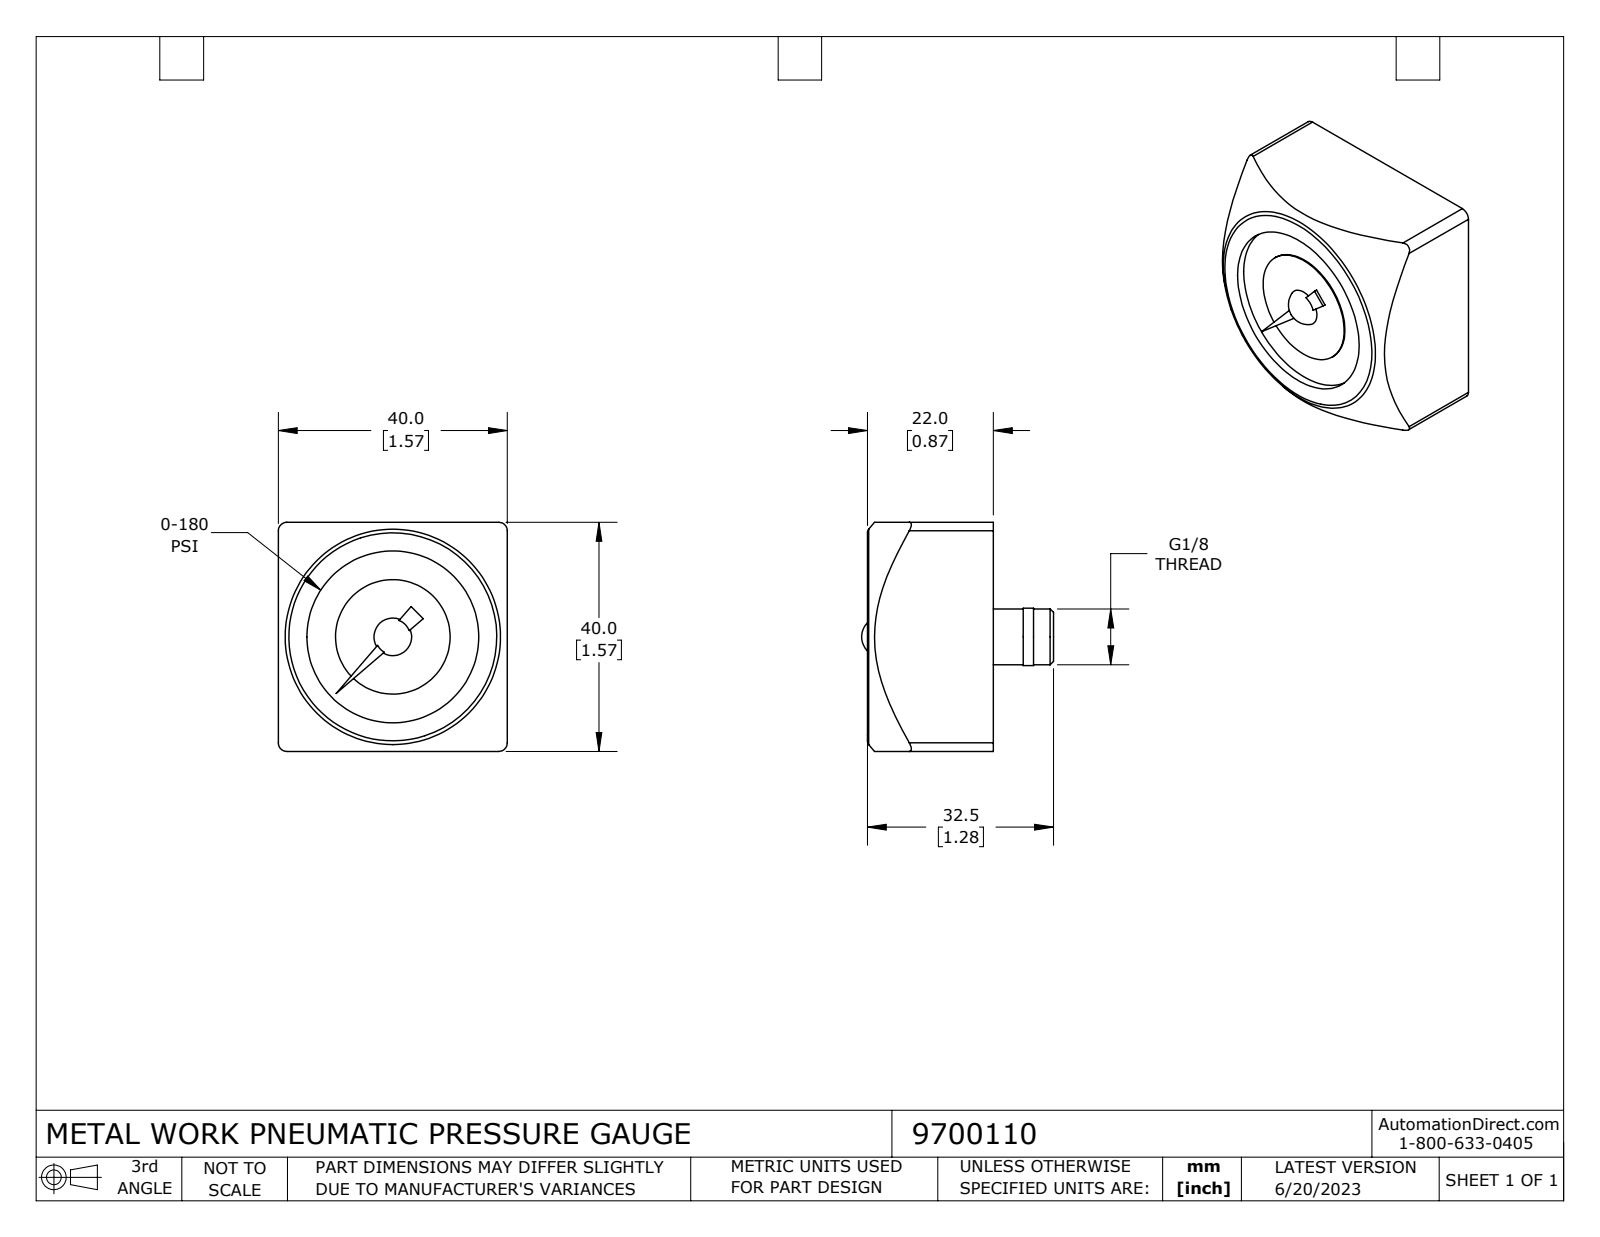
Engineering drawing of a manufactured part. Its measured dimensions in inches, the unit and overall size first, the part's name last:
Units: inches
Overall size (bounding box): 1.575 × 1.575 × 1.319
Round holes (diameter × count): ⌀1.181 ×1
Round bosses / shafts (diameter × count): ⌀0.787 ×1, ⌀0.394 ×1, ⌀0.383 ×1
Partial cylindrical surfaces — rounded edges, fillets, slot ends (radius × count): R0.059 ×4
Main face-to-face distances: 1.575, 0.807, 0.866, 0.059, 0.815, 0.051, 0.413, 1.22, 1.228, 1.28
Volume: 2.059 in³ · Surface area: 10.46 in²
Bodies: 1 solid, 41 faces (19 planar, 14 cylindrical, 8 other)
Part name (STEP PRODUCT): 9700110
STEP written by: SolidWorks 2021 (CONFIG_CONTROL_DESIGN)
